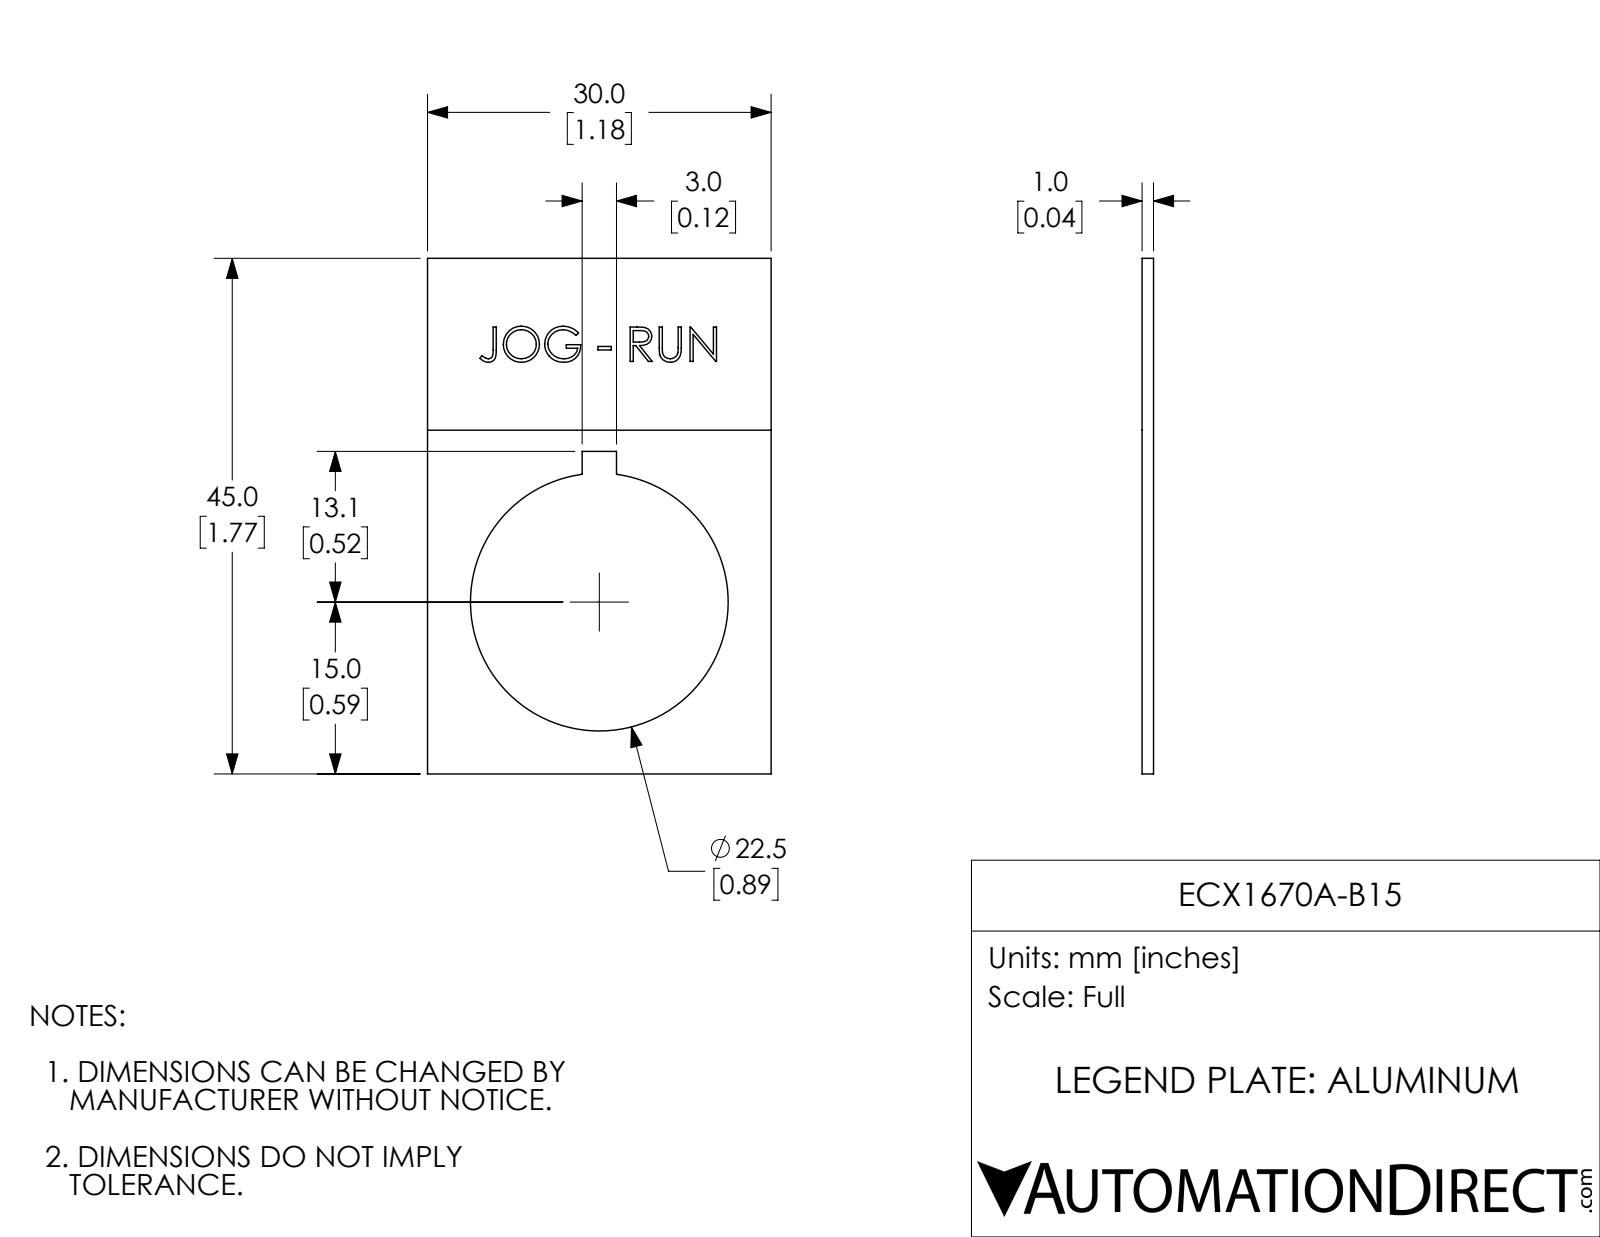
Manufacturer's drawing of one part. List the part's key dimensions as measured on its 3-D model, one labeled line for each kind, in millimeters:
Part name (STEP PRODUCT): ECX1670A-B15
STEP written by: SolidWorks 2017 (AUTOMOTIVE_DESIGN)
Units: millimetres
Bodies: 1 solid, 95 faces (58 planar, 3 cylindrical, 34 other)
Overall size (bounding box): 45 × 30 × 1
Volume: 950 mm³ · Surface area: 2 121 mm²
Round holes (diameter × count): ⌀22.5 ×1
Main face-to-face distances: 1, 30, 45, 1, 13.5, 16.5, 28.1, 16.8, 3, 4.2
